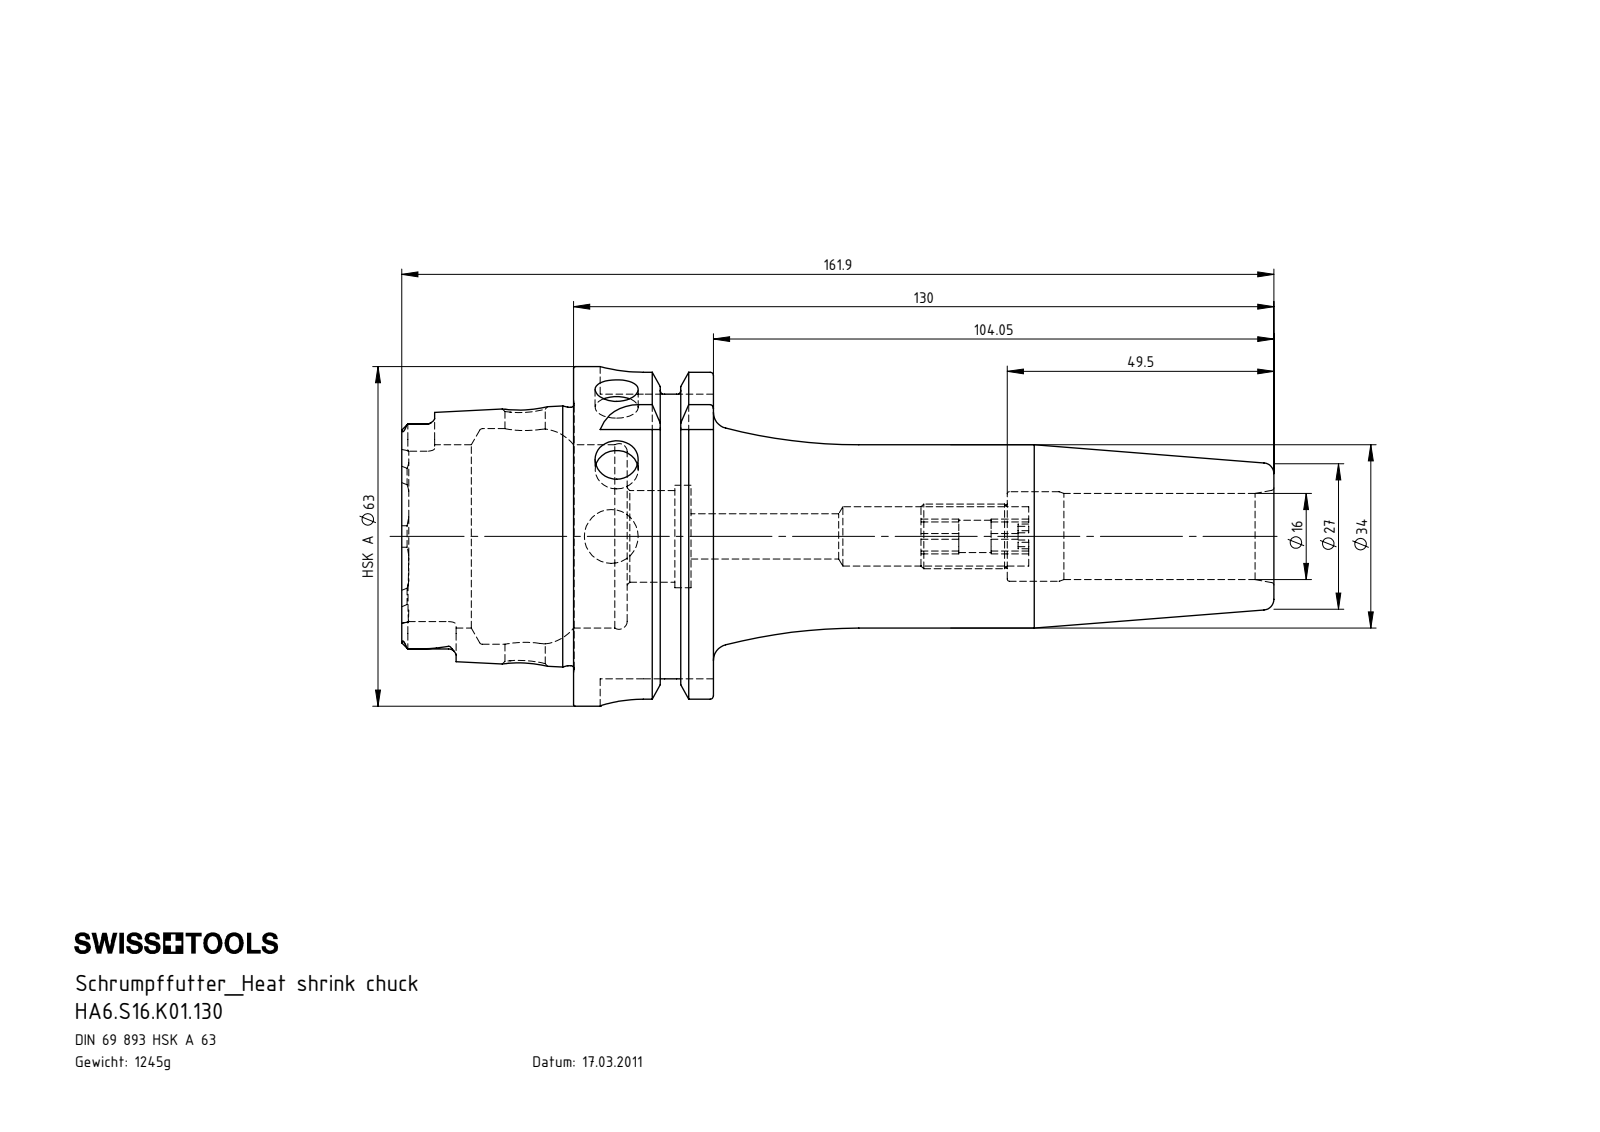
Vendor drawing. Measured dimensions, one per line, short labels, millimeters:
name: HA6-S16.K01.130; ERU-AN5.K01.020_A; HA6-S16.K01.130_A_Fertigbearbeitung
written by: SolidWorks 2012 (AUTOMOTIVE_DESIGN)
unit: mm
bodies: 2 solids, 238 faces (82 planar, 61 cylindrical, 95 other)
size: 161.9 × 63 × 63
volume: 158 545 mm³; area: 37 814 mm²
holes: 2× ⌀8, 1× ⌀6, 1× ⌀7.5, 1× ⌀8.4, 1× ⌀10, 1× ⌀11, 1× ⌀16, 1× ⌀16.6, 1× ⌀17, 1× ⌀19, 1× ⌀34, 1× ⌀40
bosses: 1× ⌀63, 1× ⌀54.95, 1× ⌀47.94, 1× ⌀12
rounds: 6× R1.4, 4× R2.88, 4× R8
face distances: 25.95, 16, 9.95, 31.9, 41.85, 57.85, 52.8, 21.8, 11.85, 53.7
